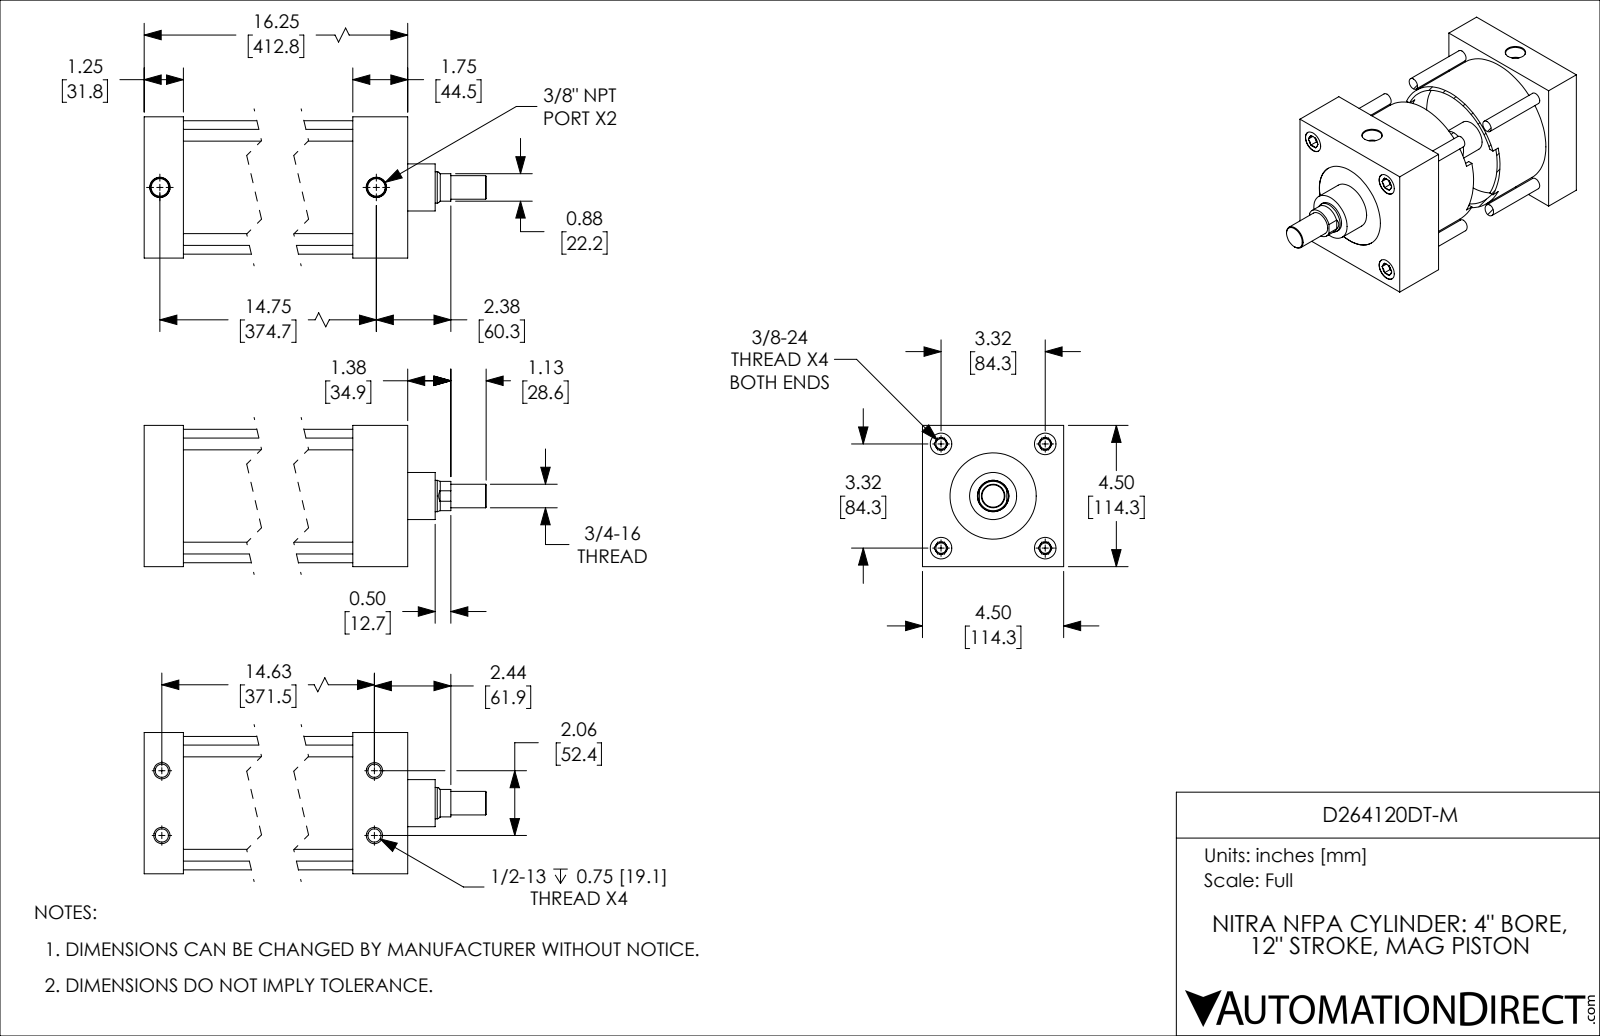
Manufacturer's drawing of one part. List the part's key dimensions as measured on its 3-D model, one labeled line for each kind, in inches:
Part name (STEP PRODUCT): D264120DT-M_BODY; D264120DT-M_PISTON_KK1; D264120DT-M
STEP written by: SolidWorks 2019 (CONFIG_CONTROL_DESIGN)
Units: inches
Bodies: 2 solids, 198 faces (58 planar, 62 cylindrical, 78 other)
Overall size (bounding box): 18.75 × 4.5 × 4.5
Volume: 113.2 in³ · Surface area: 658.3 in²
Round holes (diameter × count): ⌀0.332 ×4, ⌀0.422 ×4, ⌀0.687 ×4, ⌀0.562 ×2, ⌀1.001 ×1, ⌀2.75 ×1, ⌀4.001 ×1
Round bosses / shafts (diameter × count): ⌀0.375 ×4, ⌀4.251 ×1, ⌀3.999 ×1, ⌀1.5 ×1, ⌀0.999 ×1, ⌀0.75 ×1
Partial cylindrical surfaces — rounded edges, fillets, slot ends (radius × count): R0.469 ×1
Main face-to-face distances: 1.25, 4.5, 14.5, 13.25, 16.25, 15, 1.75, 2.5, 12, 13.75
Hole centre spacings: 2.347, 3.32, 14.724, 1.033, 4.695, 14.625, 1.034, 2.062
